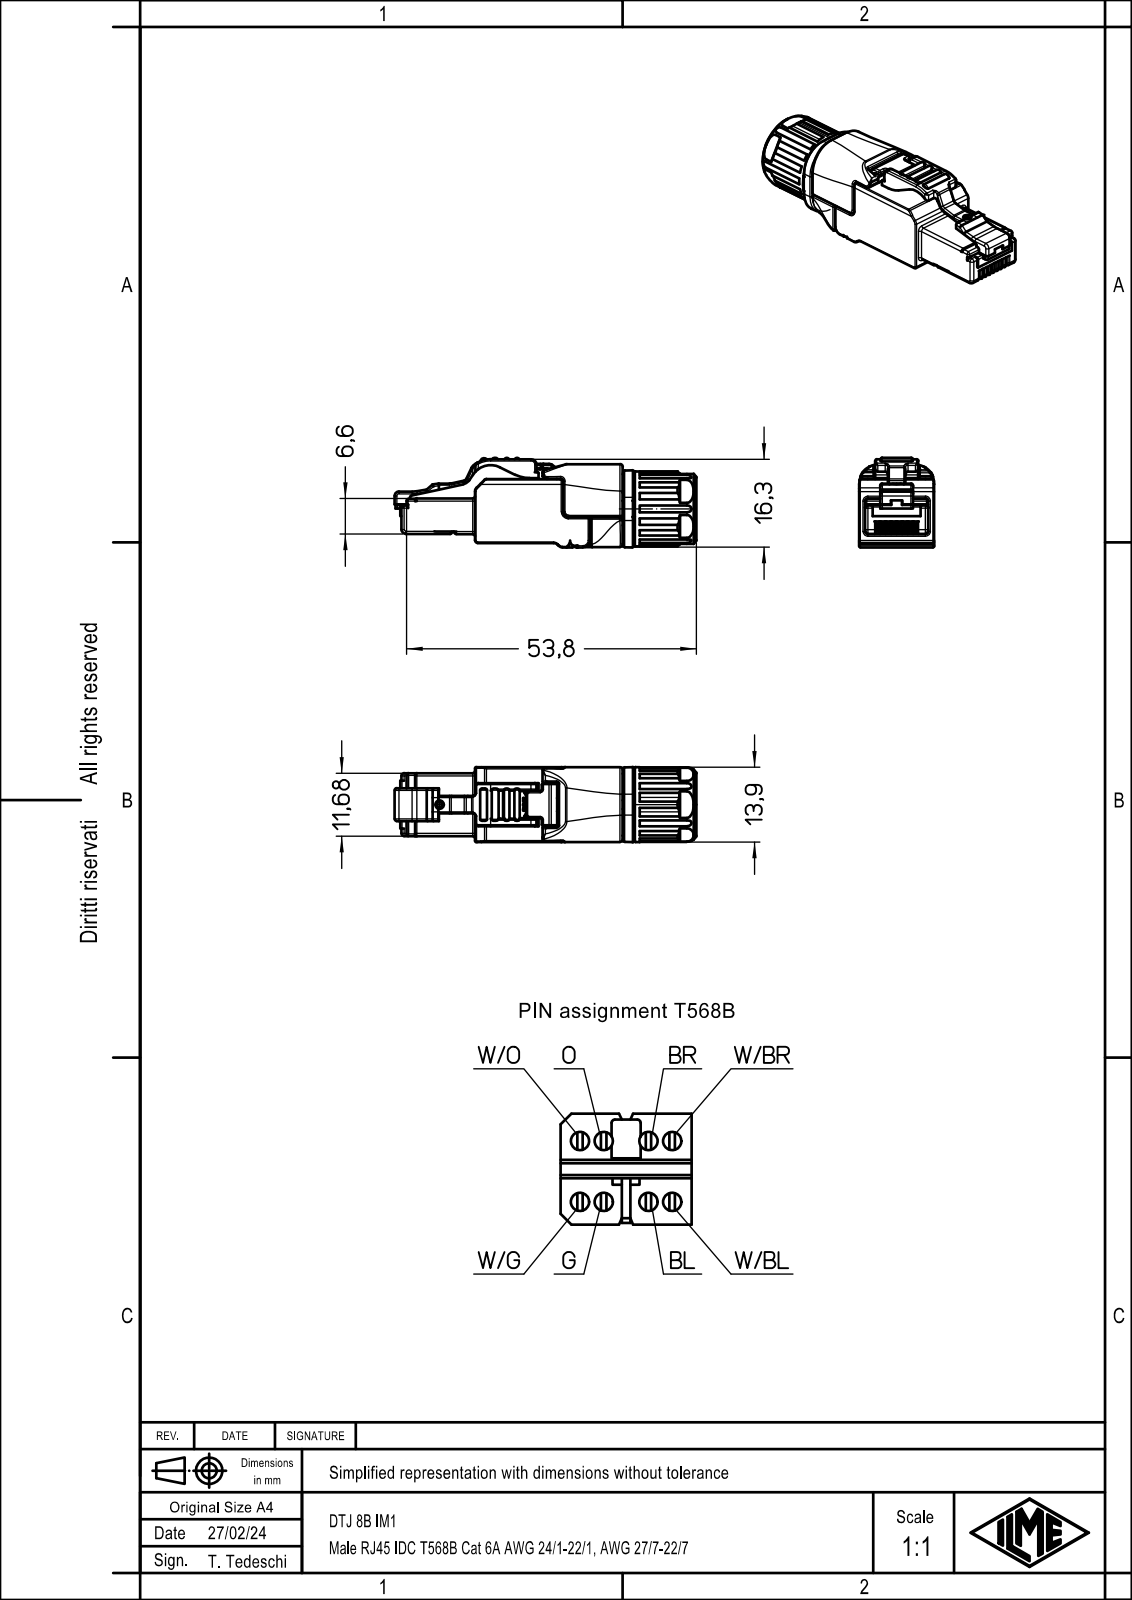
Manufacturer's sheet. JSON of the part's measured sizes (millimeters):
{"part_name": "DTJ_8B_IM1", "step_written_by": "Creo Elements/Direct Modeling 20.5B 27-May-2023 (C) Parametric Technology GmbH (AUTOMOTIVE_DESIGN)", "units": "millimeters", "bodies": {"solids": 1, "faces": 1582, "planar": 746, "cylindrical": 524, "other": 312}, "overall_size": [55.98, 16.63, 13.9], "volume_mm3": 8198, "surface_area_mm2": 4399, "round_bosses_or_shafts": [[13.9, 1], [13, 1]], "partial_cylinders_radius": [[0.3, 120], [0.5, 49], [0.7, 32], [0.2, 28], [0.4, 19], [0.23, 18], [1.25, 18], [1, 15]], "face_to_face_distances": [13.9, 0.75, 11.7, 1, 10.95, 1.11, 12.79, 2.6, 10.7, 8.1]}
